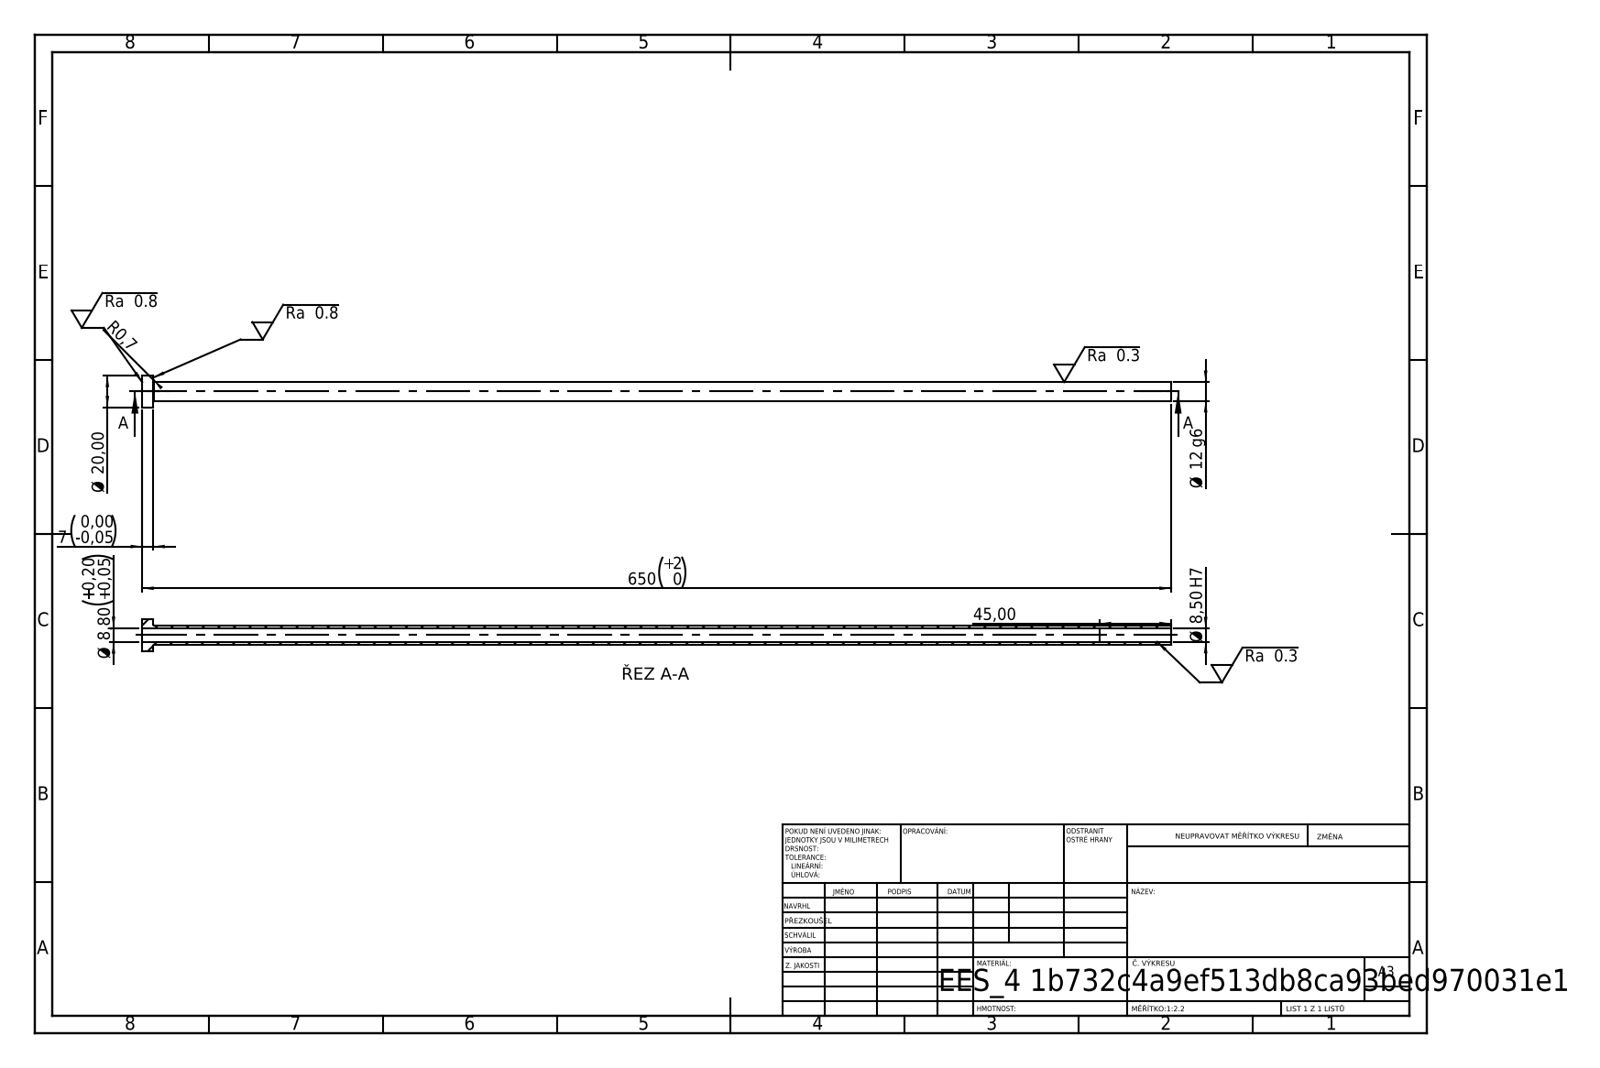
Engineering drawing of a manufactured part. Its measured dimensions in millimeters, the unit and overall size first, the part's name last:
Units: millimetres
Overall size (bounding box): 650 × 20 × 20
Round holes (diameter × count): ⌀8.5 ×1, ⌀8.8 ×1
Round bosses / shafts (diameter × count): ⌀20 ×1, ⌀12 ×1
Main face-to-face distances: 7, 650, 643, 605, 598, 45
Volume: 35 574 mm³ · Surface area: 43 112 mm²
Bodies: 1 solid, 14 faces (4 planar, 8 cylindrical, 2 other)
STEP written by: SolidWorks 2019 (CONFIG_CONTROL_DESIGN)
